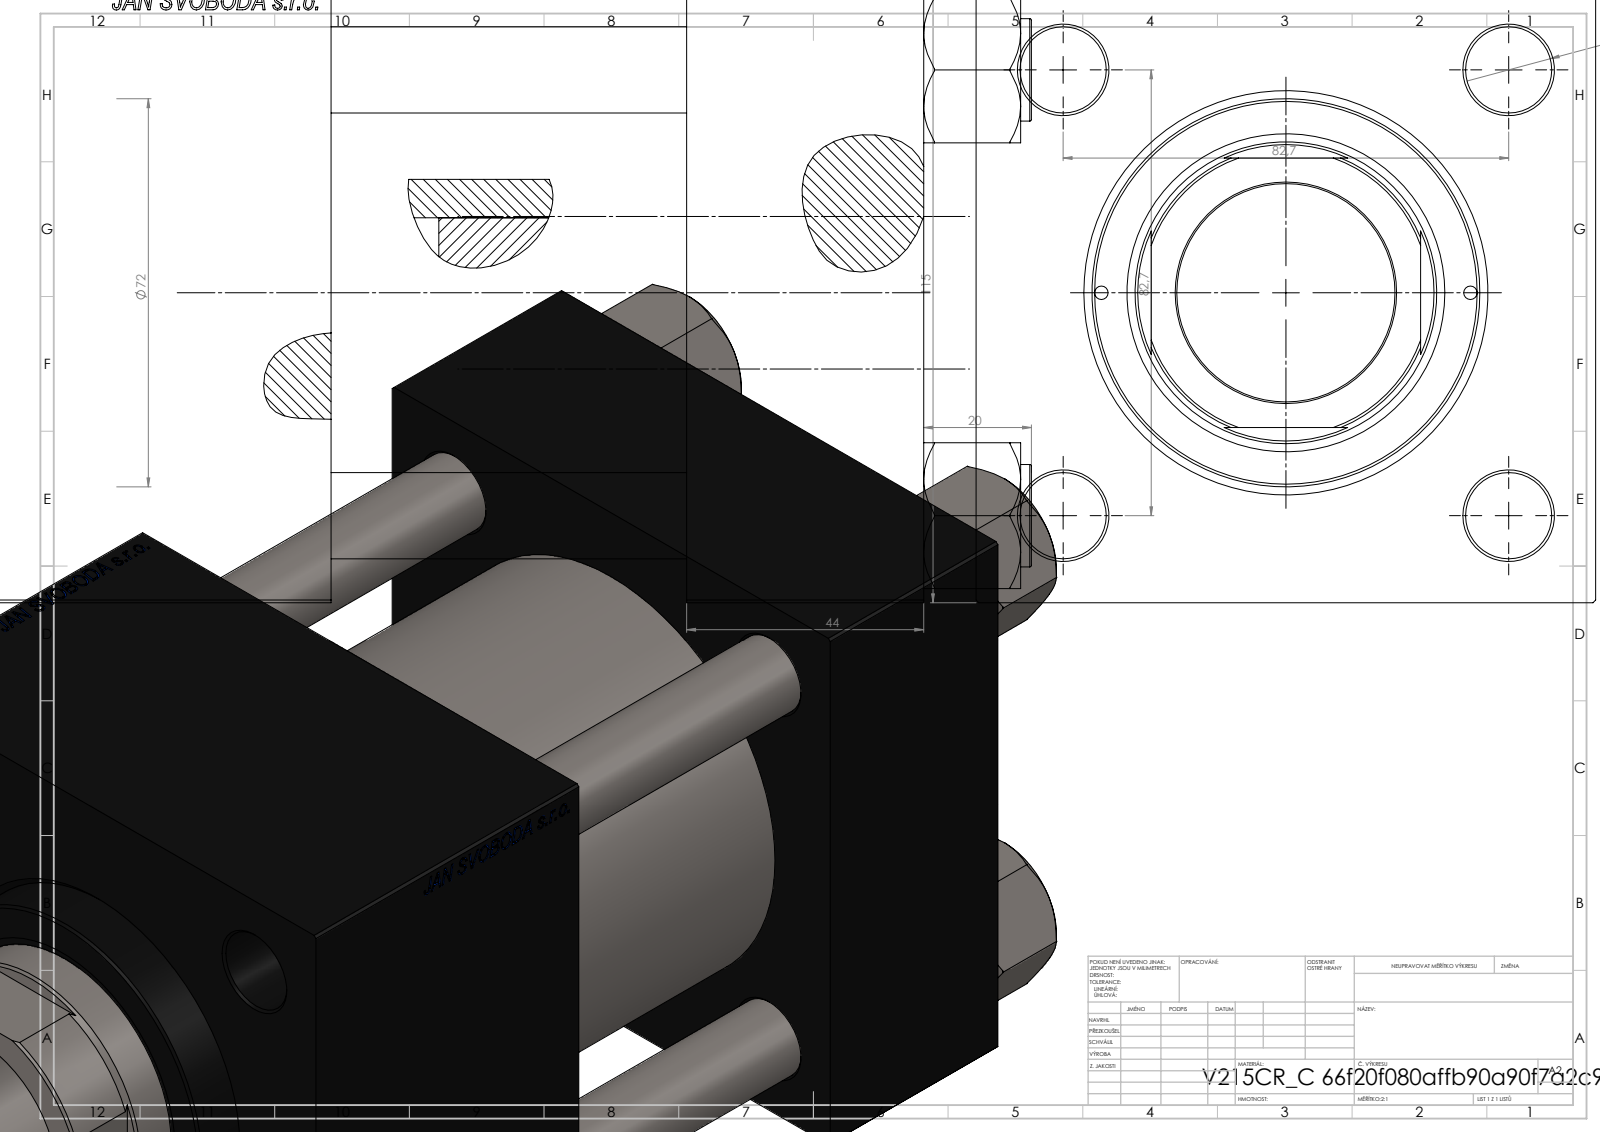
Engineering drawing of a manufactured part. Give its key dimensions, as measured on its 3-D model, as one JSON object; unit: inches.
{"part_name": "NUT_M5_C; V215CR_C_TYCINKA; V215_VC_A; V215CR_VCP_C (+1 more)", "step_written_by": "SolidWorks 2019 (CONFIG_CONTROL_DESIGN)", "units": "inches", "bodies": {"solids": 11, "faces": 1200, "planar": 575, "cylindrical": 89, "other": 536}, "overall_size": [9.055, 4.528, 4.528], "volume_in3": 113.6, "surface_area_in2": 434.7, "round_holes": [[0.63, 4], [0.098, 2], [0.276, 2], [1.041, 2], [1.378, 2], [1.594, 1], [2.205, 1], [2.323, 1], [2.402, 1], [2.835, 1], [3.15, 1]], "round_bosses_or_shafts": [[0.748, 4], [3.386, 1]], "partial_cylinders_radius": [[1.063, 1]], "face_to_face_distances": [4.528, 1.732, 4.331, 2.598, 7.047, 5.315, 2.717, 0.787, 5.917, 4.185], "hole_center_spacings": [1.652, 2.302, 3.256, 3.393, 1.348, 4.605, 2.697]}
